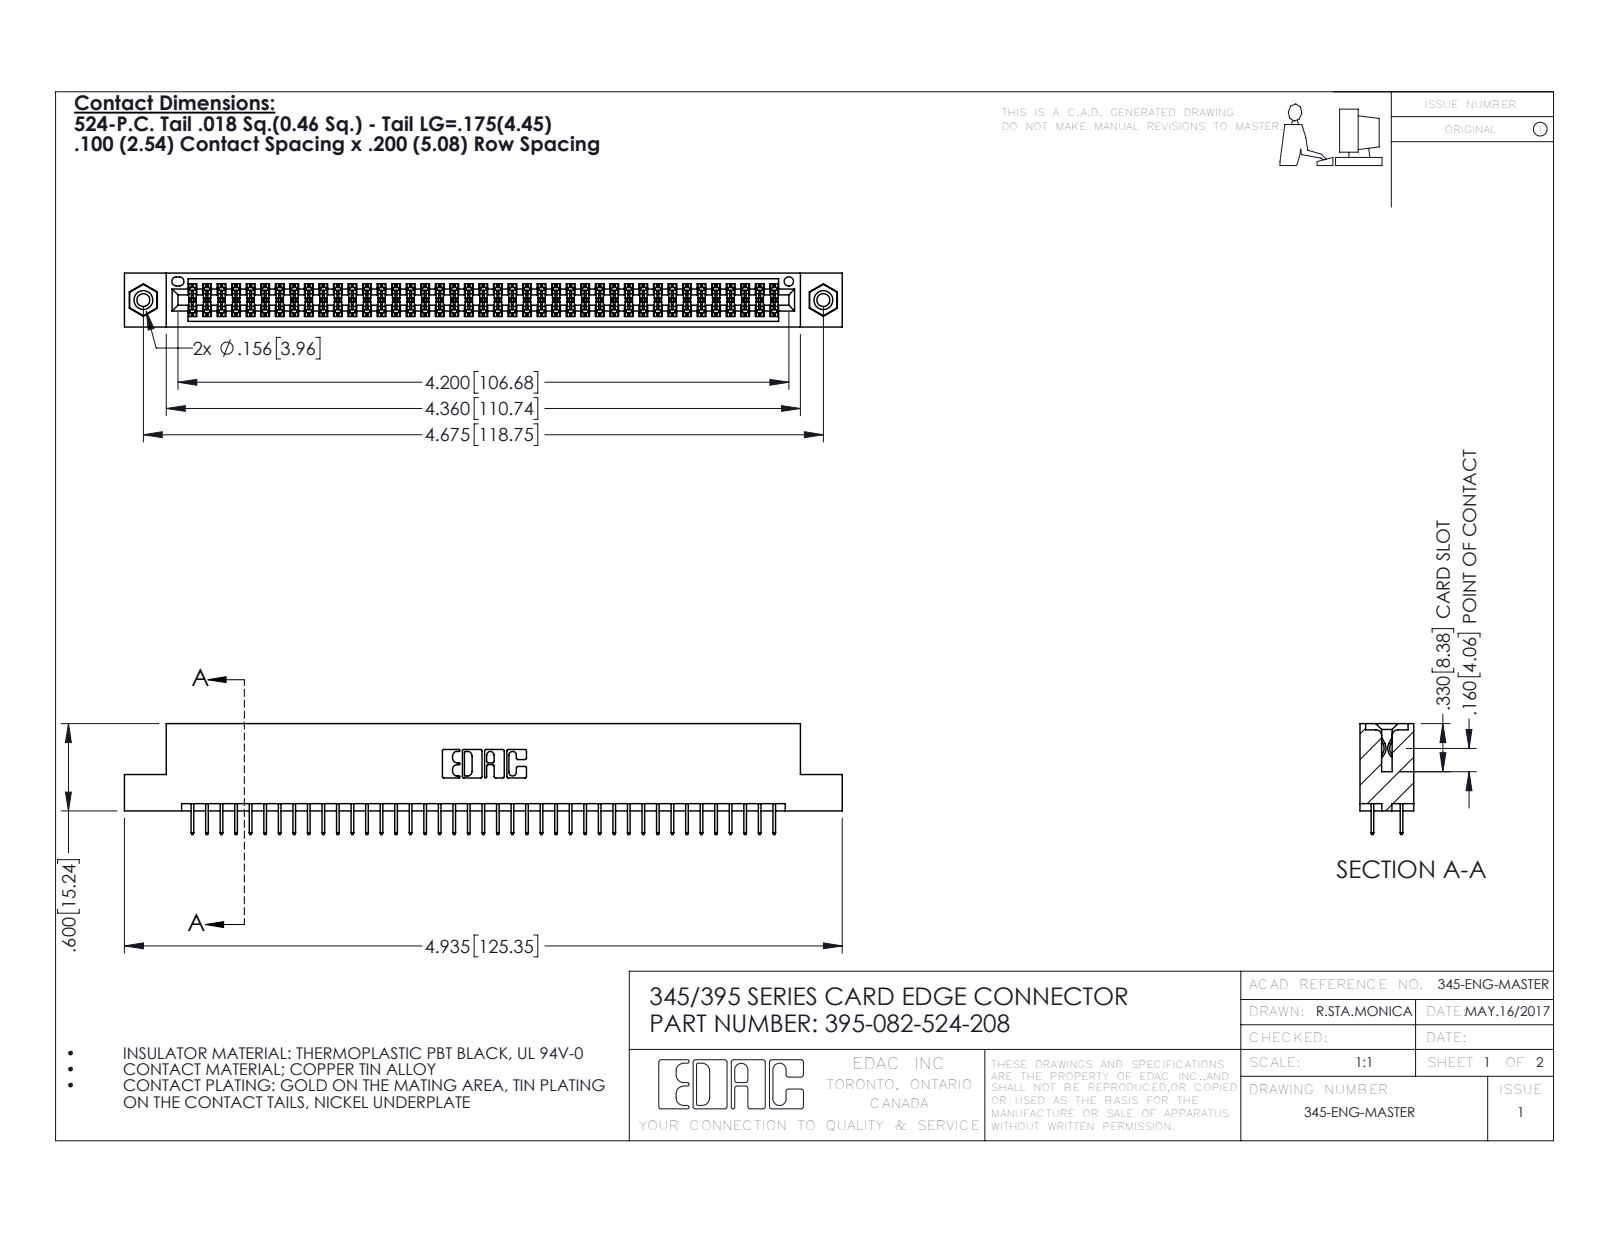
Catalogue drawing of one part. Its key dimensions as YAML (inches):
part_name: "395-082-524-208; 345-292-001_345-293-124; 345-250-001_345-250-003-102; 345 Part_Flush Mounting Lugs - 0.156 Dia-TI"
step_written_by: "SolidWorks 2016 (CONFIG_CONTROL_DESIGN)"
units: inches
bodies: {solids: 85, faces: 4614, planar: 3310, cylindrical: 1288, other: 16}
overall_size: [4.935, 0.762, 0.37]
volume: 0.735
surface_area: 27.06
round_holes:
  - {diameter: 0.089, count: 2}
  - {diameter: 0.125, count: 2}
  - {diameter: 0.156, count: 2}
  - {diameter: 0.064, count: 1}
round_bosses_or_shafts:
  - {diameter: 0.155, count: 2}
partial_cylinders:
  - {radius: 0.006, count: 123}
  - {radius: 0.01, count: 22}
  - {radius: 0.007, count: 6}
  - {radius: 0.031, count: 6}
  - {radius: 0.026, count: 3}
  - {radius: 0.014, count: 2}
  - {radius: 0.019, count: 2}
  - {radius: 0.022, count: 2}
face_to_face_distances: [0.072, 0.298, 0.2, 0.37, 0.098, 0.272, 0.025, 0.225, 0.072, 0.175]
hole_center_spacings: [0.27, 4.439, 4.675]
